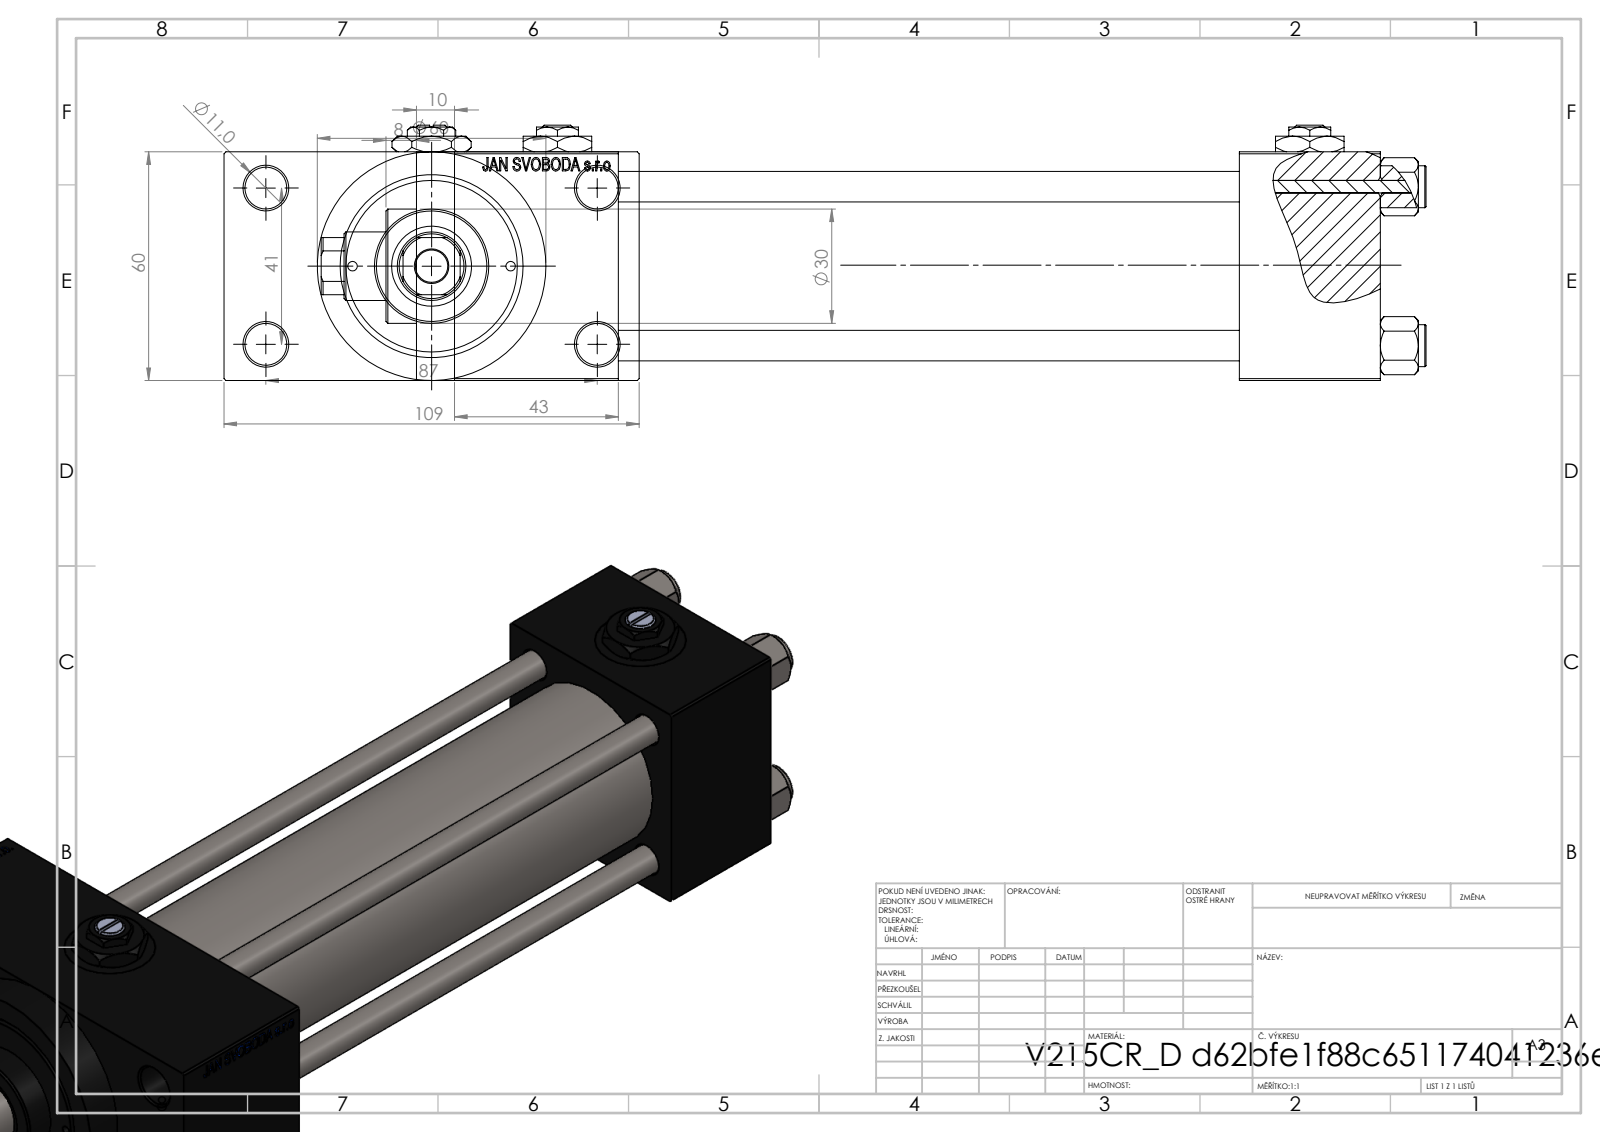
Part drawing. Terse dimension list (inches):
name: V215CR_D_TYCINKA; V215_VC_A; V215CR_VCP_D; V215CR_D_Body (+2 more)
written by: SolidWorks 2019 (CONFIG_CONTROL_DESIGN)
unit: in
bodies: 13 solids, 1214 faces (548 planar, 104 cylindrical, 562 other)
size: 11.417 × 4.291 × 2.638
volume: 36.97 in³; area: 261.5 in²
holes: 4× ⌀0.315, 4× ⌀0.433, 2× ⌀0.098, 2× ⌀0.276, 2× ⌀0.656, 2× ⌀0.945, 1× ⌀0.335, 1× ⌀0.709, 1× ⌀0.827, 1× ⌀1.22, 1× ⌀1.575, 1× ⌀1.772
bosses: 4× ⌀0.433, 1× ⌀2.362, 1× ⌀1.811, 1× ⌀1.181
rounds: 1× R0.335
face distances: 2.362, 0.965, 3.327, 6.417, 1.457, 7.874, 1.693, 9.567, 8.11, 4.291
hole spacings: 0.821, 0.892, 1.161, 1.206, 1.642, 1.832, 1.856, 1.893
